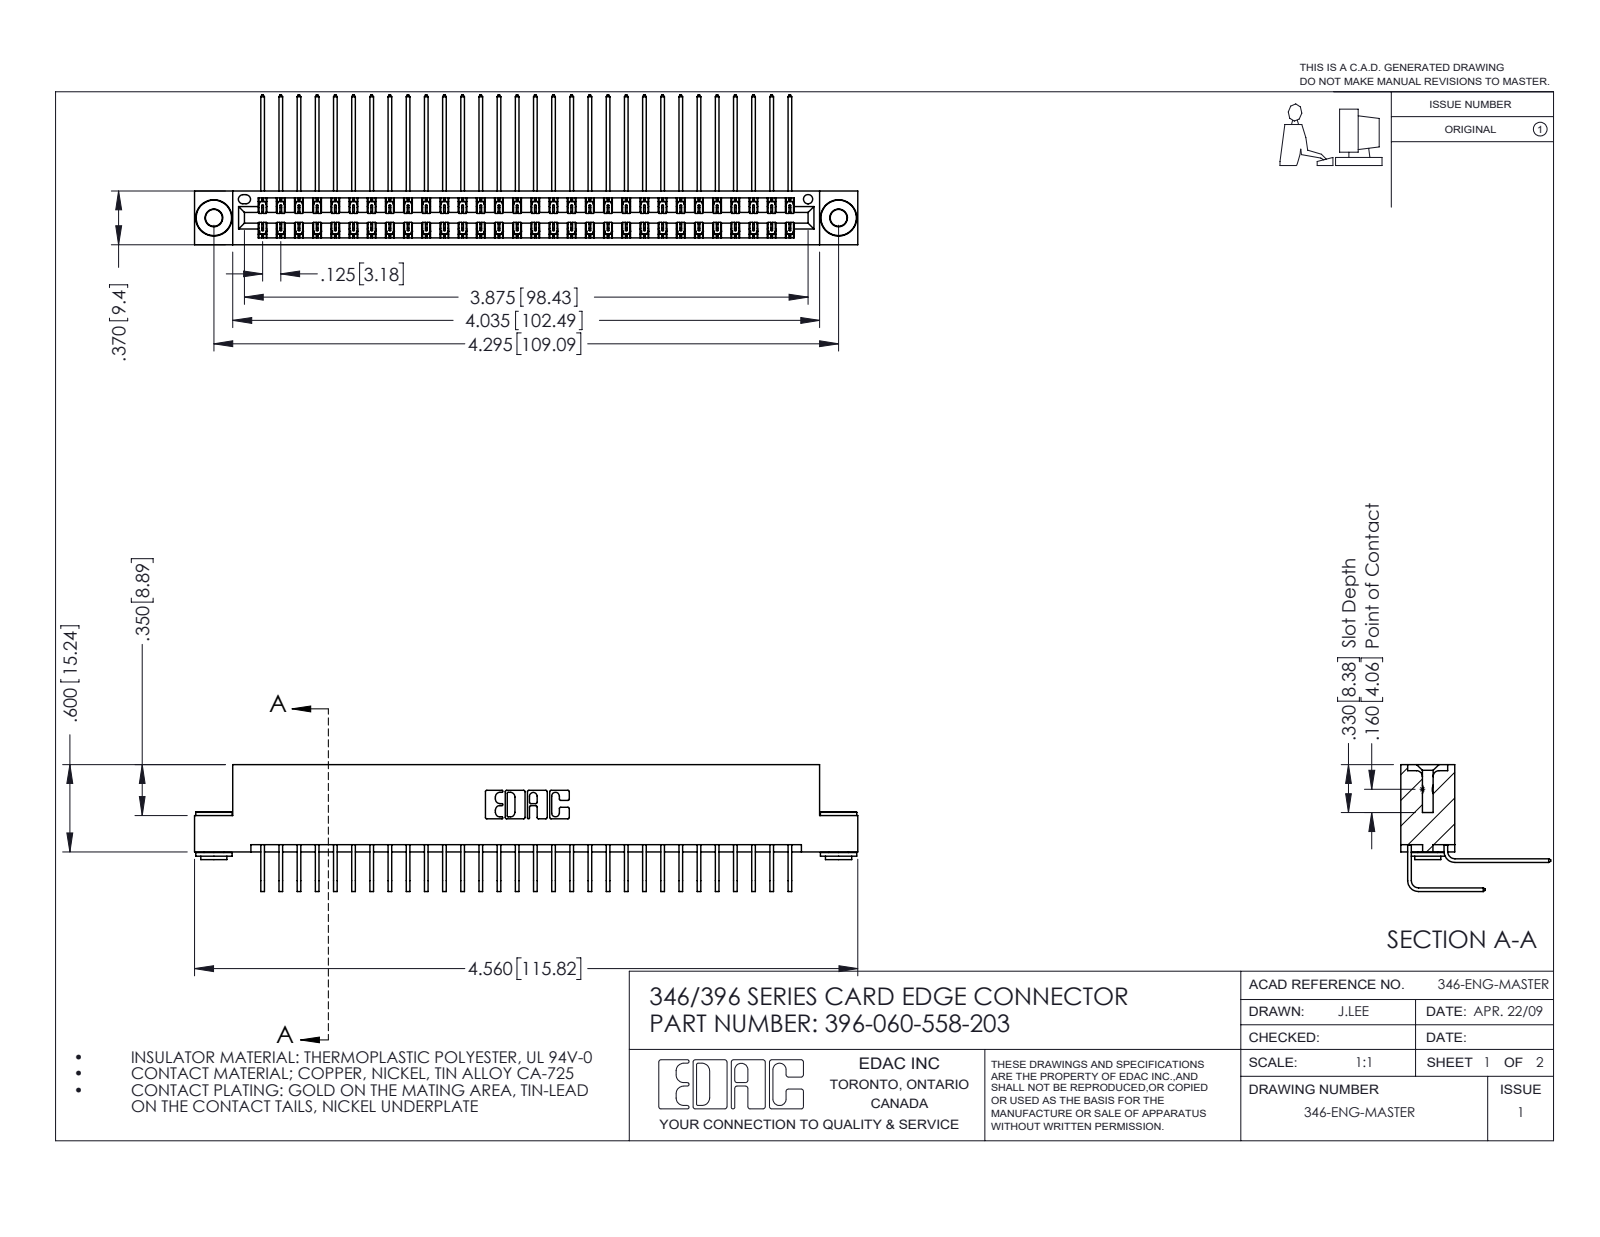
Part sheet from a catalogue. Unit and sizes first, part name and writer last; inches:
Units: inches
Overall size (bounding box): 4.56 × 1.03 × 0.873
Round holes (diameter × count): ⌀0.116 ×2, ⌀0.156 ×2, ⌀0.064 ×1
Round bosses / shafts (diameter × count): ⌀0.25 ×2, ⌀0.18 ×2, ⌀0.136 ×2
Partial cylindrical surfaces — rounded edges, fillets, slot ends (radius × count): R0.006 ×90, R0.01 ×22, R0.007 ×6, R0.031 ×6, R0.026 ×3, R0.014 ×2, R0.022 ×2, R0.024 ×2
Main face-to-face distances: 0.322, 0.048, 0.025, 0.25, 0.37, 0.298, 0.072, 0.275, 0.148, 0.222
Hole centre spacings: 0.246, 4.087, 4.295
Volume: 0.706 in³ · Surface area: 27.26 in²
Bodies: 63 solids, 3400 faces (2306 planar, 1086 cylindrical, 8 other)
Part name (STEP PRODUCT): 345-250-002_345-250-002-102; 345-292-001_558 Tail - 2; 396-060-558-203; 346 Part_Flush Mounting Lugs - 0.156 Dia-TH (+1 more)
STEP written by: SolidWorks 2016 (CONFIG_CONTROL_DESIGN)
